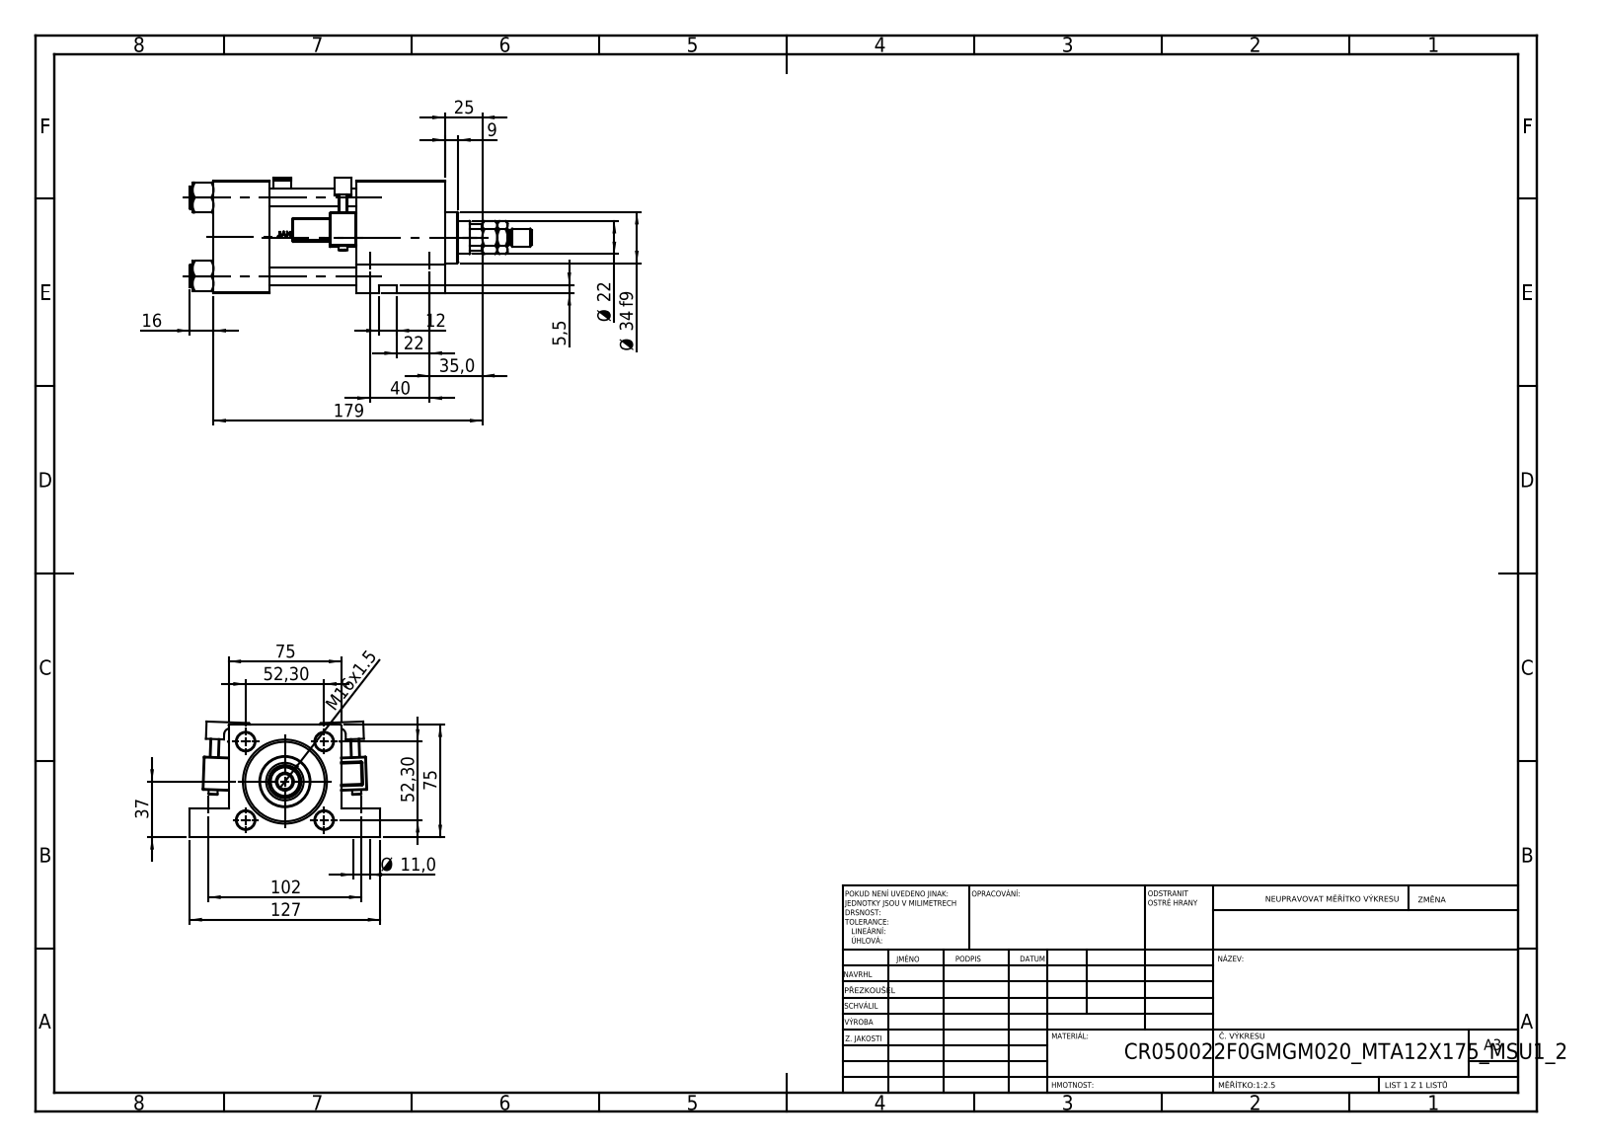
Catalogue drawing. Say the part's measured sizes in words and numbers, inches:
The part is named "V215CR_F_Body; V215CR_F_TYCINKA; MTA; V215CR_MSU (+3 more)". Its 3-D file was written by "SolidWorks 2019 (CONFIG_CONTROL_DESIGN)". It is 14 solids with 1306 faces: 510 planar, 190 cylindrical and 606 other. Overall it measures 8.976 by 5 by 3.033 inches. Its volume is 46.06 cubic inches and its surface area 265 square inches. Round holes: 4 of diameter 0.472, 2 of diameter 0.276, 2 of diameter 0.433, 2 of diameter 0.433, 2 of diameter 1.181, 1 of diameter 0.413, 1 of diameter 0.669, 1 of diameter 0.825, 1 of diameter 0.866, 1 of diameter 0.984, 1 of diameter 1.614, 1 of diameter 1.969. Round bosses or shafts: 4 of diameter 0.591, 2 of diameter 0.236, 1 of diameter 2.205, 1 of diameter 1.339, 1 of diameter 0.472, 1 of diameter 0.394. Partial cylindrical surfaces (rounded edges, fillets, slot ends): 48 of radius 0.02, 2 of radius 0.039, 2 of radius 0.098, 2 of radius 0.157, 1 of radius 0.413. The main face-to-face distances are 2.953, 1.457, 6.063, 4.606, 3.74, 2.283, 2.323, 0.748, 2.205, 4.933. The hole center spacings are 2.059, 1.442, 1.47, 1.575, 2.912, 4.016, 4.313, 3.681.
